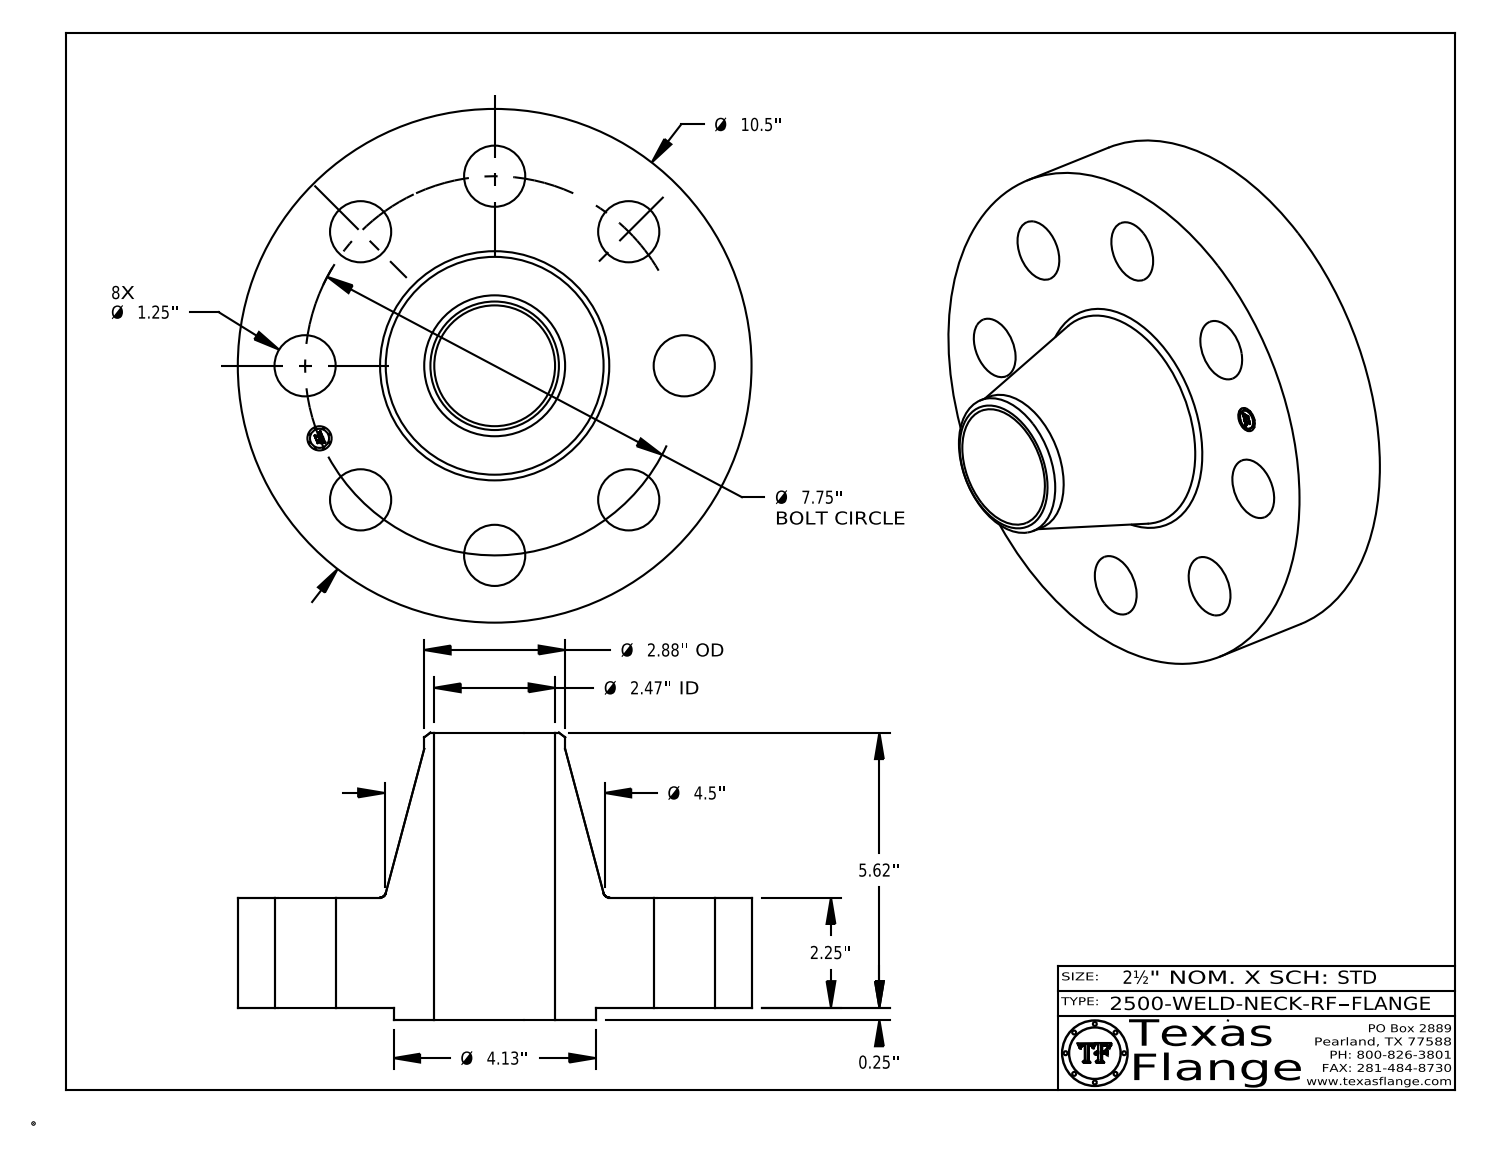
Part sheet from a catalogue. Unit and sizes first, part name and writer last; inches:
Units: inches
Overall size (bounding box): 10.5 × 10.5 × 5.87
Round holes (diameter × count): ⌀1.25 ×8, ⌀0.495 ×1, ⌀2.469 ×1
Round bosses / shafts (diameter × count): ⌀0.03 ×8, ⌀10.5 ×1, ⌀4.13 ×1, ⌀2.88 ×1, ⌀0.39 ×1
Main face-to-face distances: 2.25, 0.25, 2.5, 5.87, 5.62, 3.37, 2.485, 2.235, 0.015, 3.385
Hole centre spacings: 2.966, 3.875, 5.48, 7.16, 7.75, 7.601, 1.512, 1.512
Volume: 183.1 in³ · Surface area: 366.8 in²
Bodies: 1 solid, 419 faces (369 planar, 44 cylindrical, 6 other)
Part name (STEP PRODUCT): 2500-WELD-NECK-RF
STEP written by: CATIA V5 STEP AP214 (AUTOMOTIVE_DESIGN)
